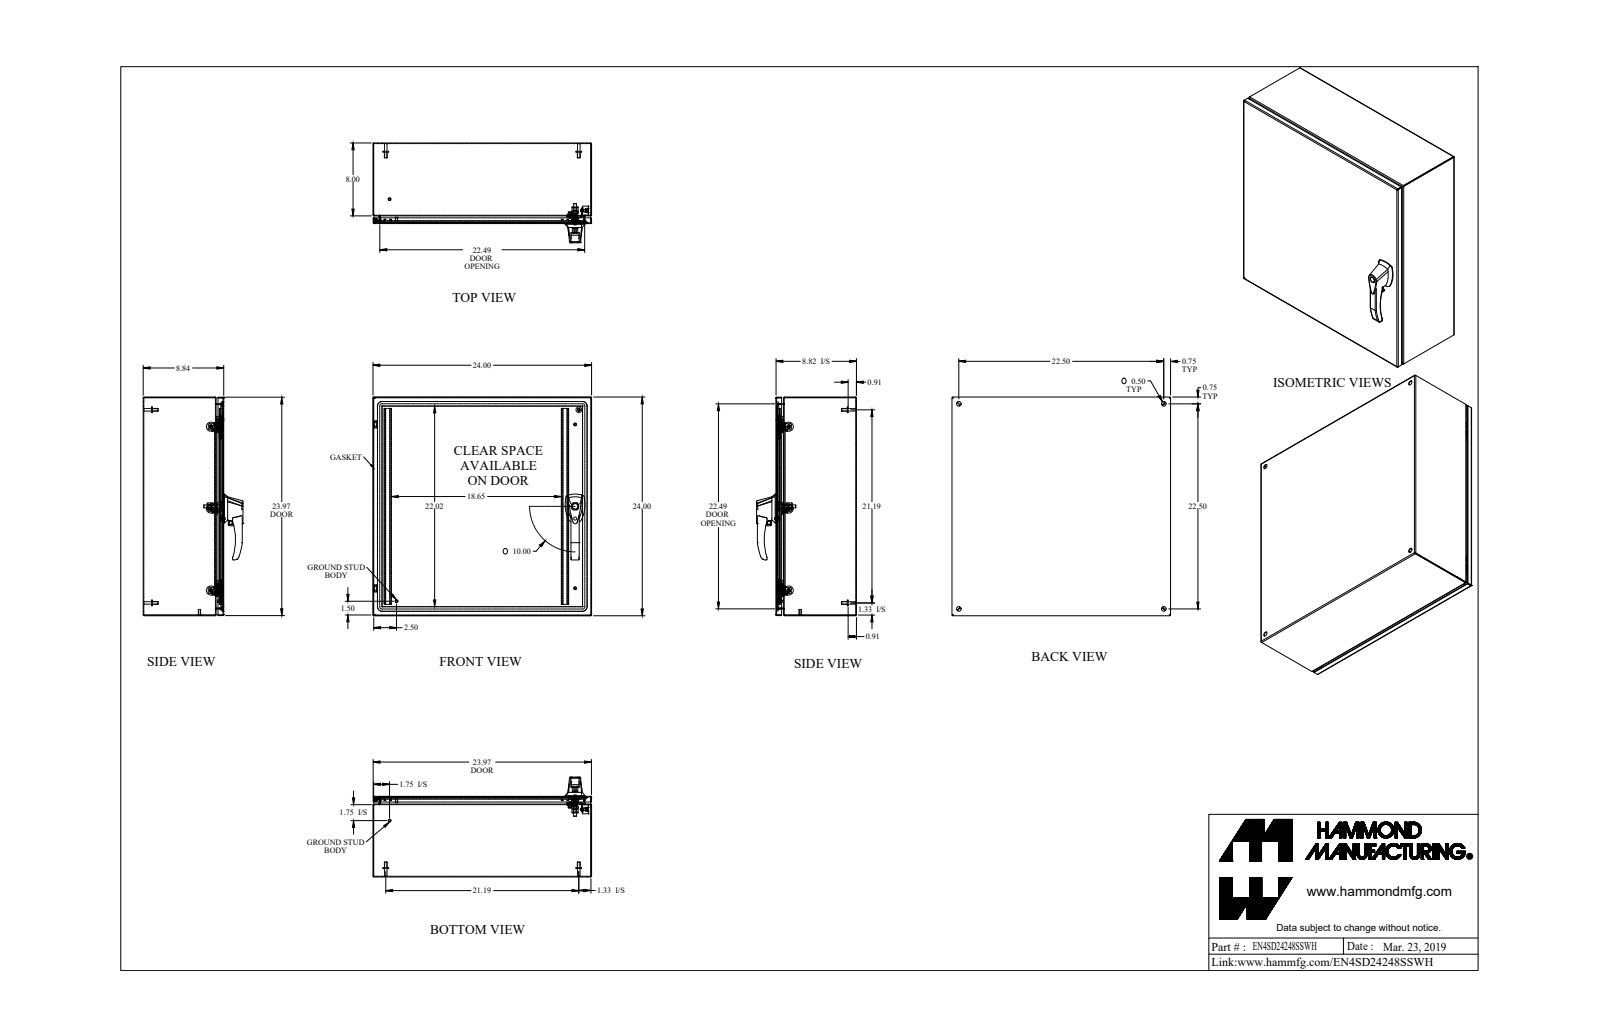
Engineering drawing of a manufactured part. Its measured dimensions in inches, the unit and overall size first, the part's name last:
Units: inches
Overall size (bounding box): 24 × 24 × 10.958
Round holes (diameter × count): ⌀0.176 ×6, ⌀0.5 ×4, ⌀0.25 ×3, ⌀0.265 ×3, ⌀0.313 ×3, ⌀0.413 ×3, ⌀0.196 ×2, ⌀0.256 ×2, ⌀0.394 ×2, ⌀0.172 ×1, ⌀0.233 ×1, ⌀0.24 ×1
Round bosses / shafts (diameter × count): ⌀0.25 ×7, ⌀0.375 ×6, ⌀0.313 ×6, ⌀0.156 ×6, ⌀0.625 ×4, ⌀0.275 ×4, ⌀1 ×3, ⌀0.51 ×3
Partial cylindrical surfaces — rounded edges, fillets, slot ends (radius × count): R0.036 ×20, R0.108 ×20, R0.25 ×19, R0.01 ×12, R0.048 ×12, R0.125 ×9, R0.06 ×7, R0.03 ×6
Main face-to-face distances: 0.072, 8.771, 23.928, 8.699, 8.843, 23.856, 24, 0.843, 7.928, 0.75
Hole centre spacings: 22.5, 2.502, 8.984, 8.985, 8.985, 9, 11.3, 17.969
Volume: 178 in³ · Surface area: 4 691 in²
Bodies: 48 solids, 1265 faces (558 planar, 491 cylindrical, 216 other)
Part name (STEP PRODUCT): EN4SD24248SSWH_Default
STEP written by: SolidWorks 2019 (CONFIG_CONTROL_DESIGN)
